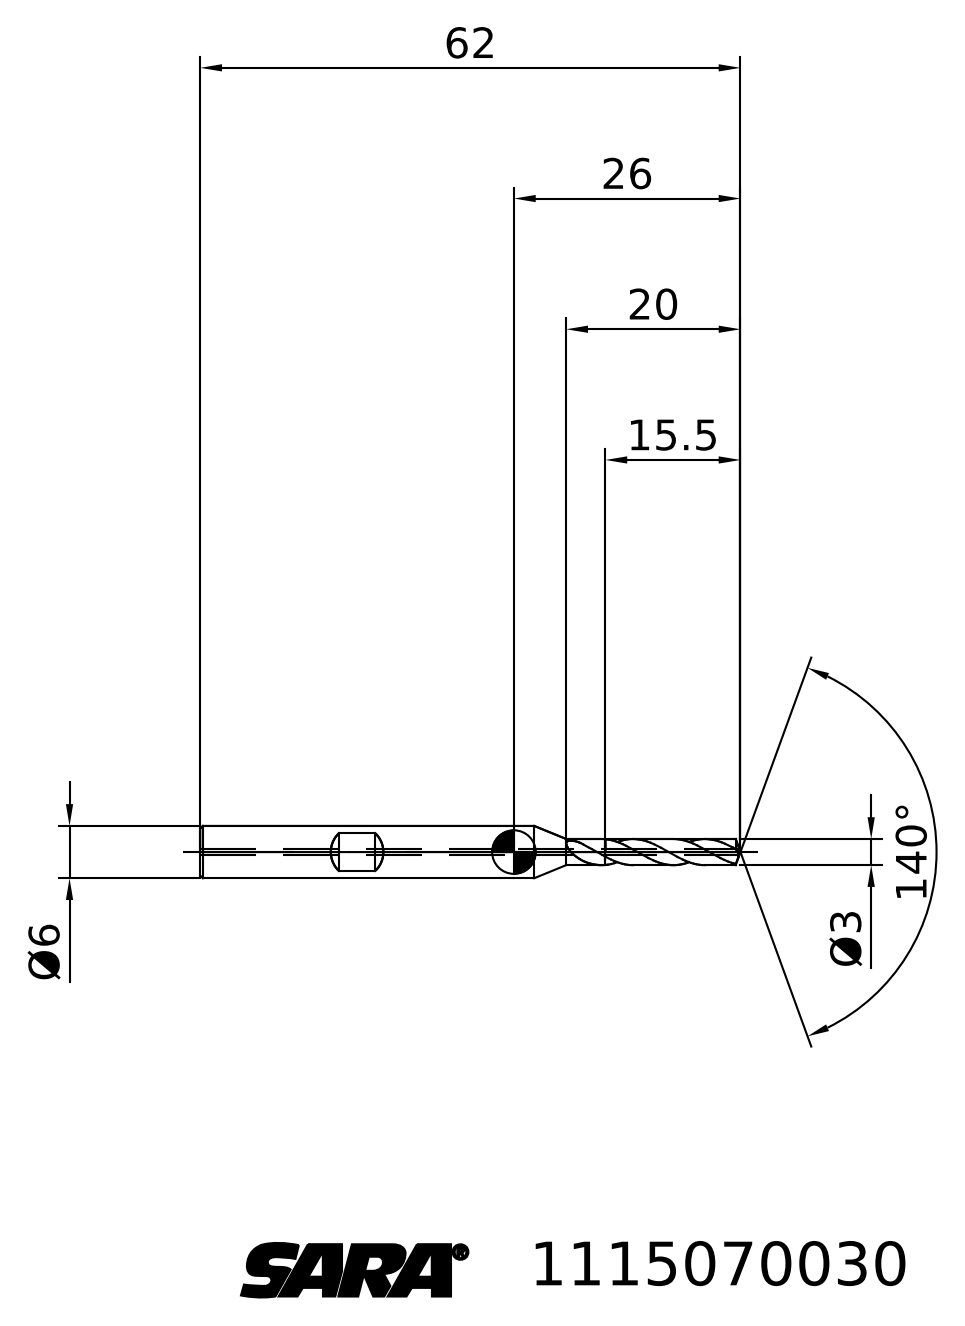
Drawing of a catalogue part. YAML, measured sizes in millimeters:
step_written_by: "TDM (AUTOMOTIVE_DESIGN)"
units: millimeters
bodies: {solids: 2, faces: 29, planar: 6, cylindrical: 0, other: 23}
overall_size: [62, 6, 6]
volume: 1223
surface_area: 1018
face_to_face_distances: [46.5]
